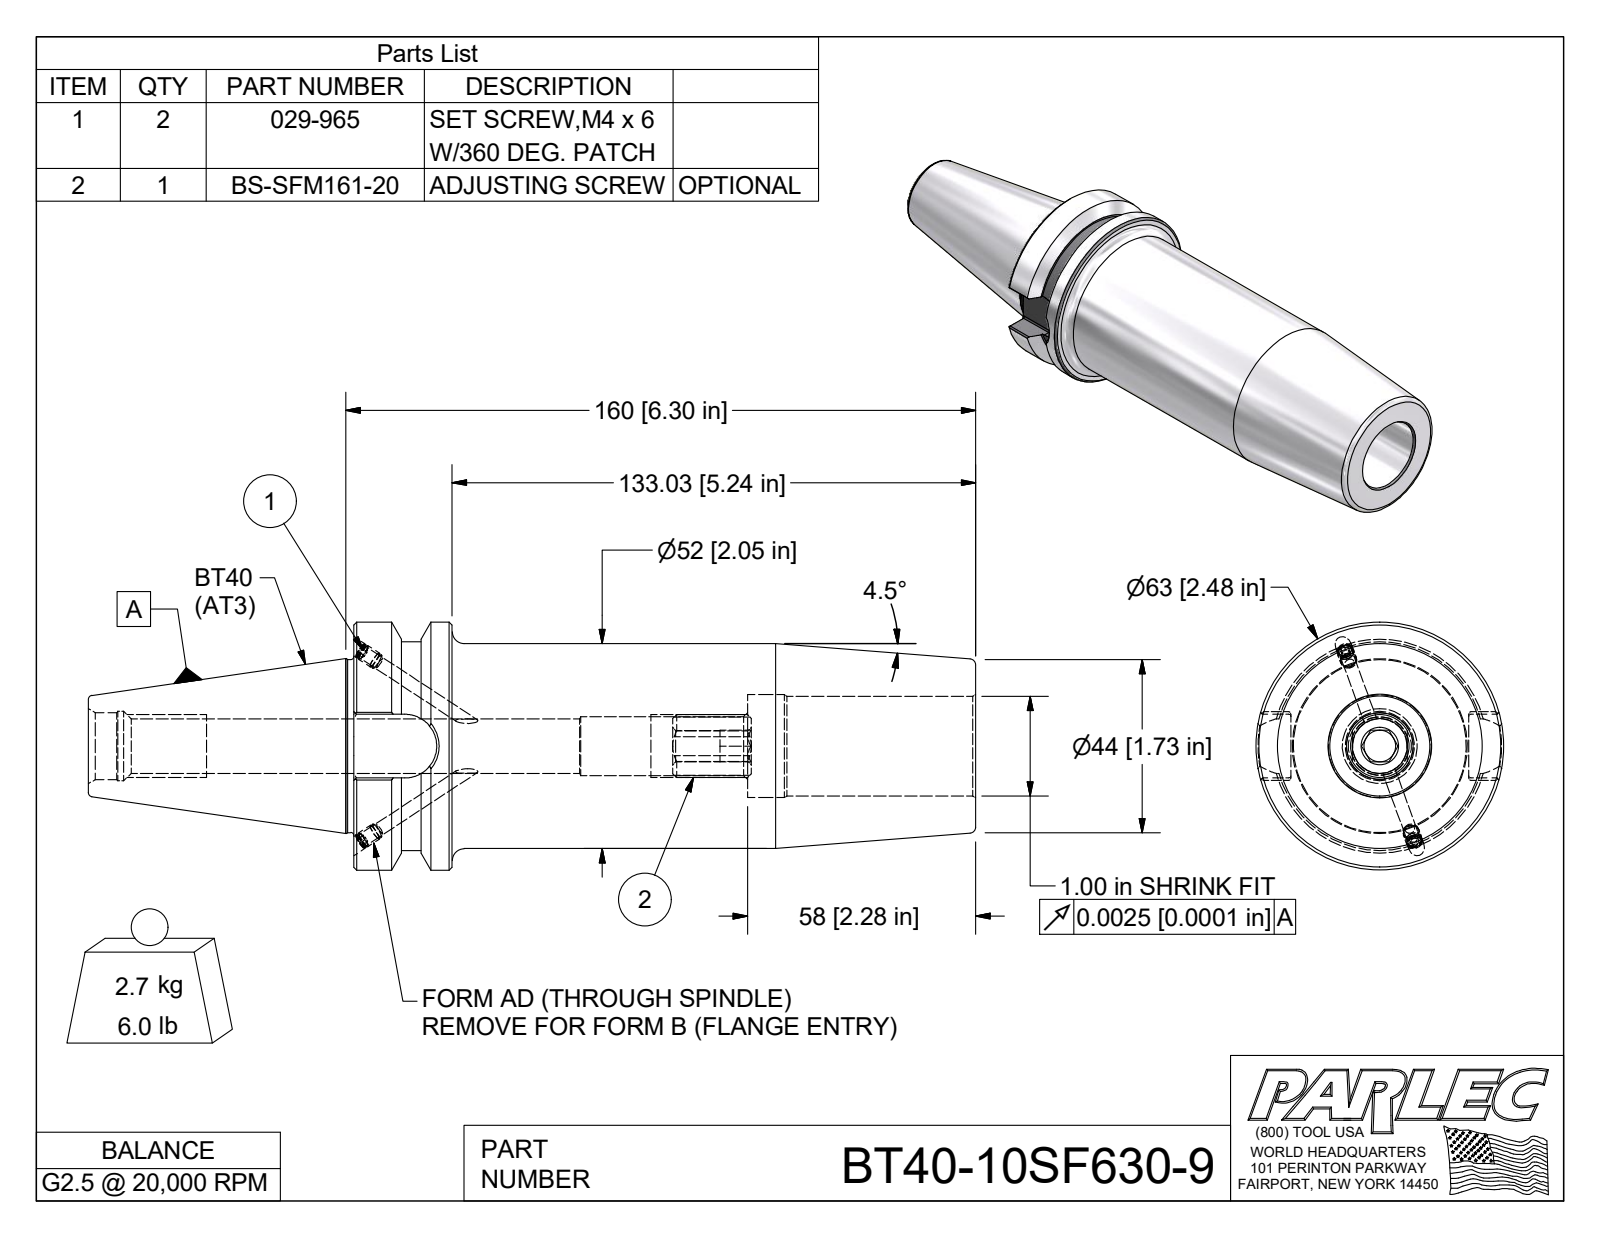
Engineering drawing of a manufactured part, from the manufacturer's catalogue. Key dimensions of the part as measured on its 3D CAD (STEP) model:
Part name (STEP PRODUCT): BT40-10SF630-9; BT40BC-10SF630-9-1; 029-965; BS-SFM161-20
STEP written by: Autodesk Inventor 2009 (AUTOMOTIVE_DESIGN)
Units: inches
Bodies: 4 solids, 131 faces (57 planar, 33 cylindrical, 41 other)
Overall size (bounding box): 8.874 × 2.48 × 2.48
Volume: 21.15 in³ · Surface area: 82.42 in²
Round holes (diameter × count): ⌀0.13 ×2, ⌀0.161 ×2, ⌀0.694 ×1, ⌀0.999 ×1, ⌀1.029 ×1
Round bosses / shafts (diameter × count): ⌀0.165 ×2, ⌀0.157 ×2, ⌀2.48 ×1, ⌀2.087 ×1, ⌀2.047 ×1, ⌀1.75 ×1, ⌀1.73 ×1
Partial cylindrical surfaces — rounded edges, fillets, slot ends (radius × count): R0.02 ×8, R0.315 ×1, R0.319 ×1
Main face-to-face distances: 6.221, 0.984, 5.237, 3.938, 2.954, 2.283, 0.615, 1.166, 1.78, 2.653
